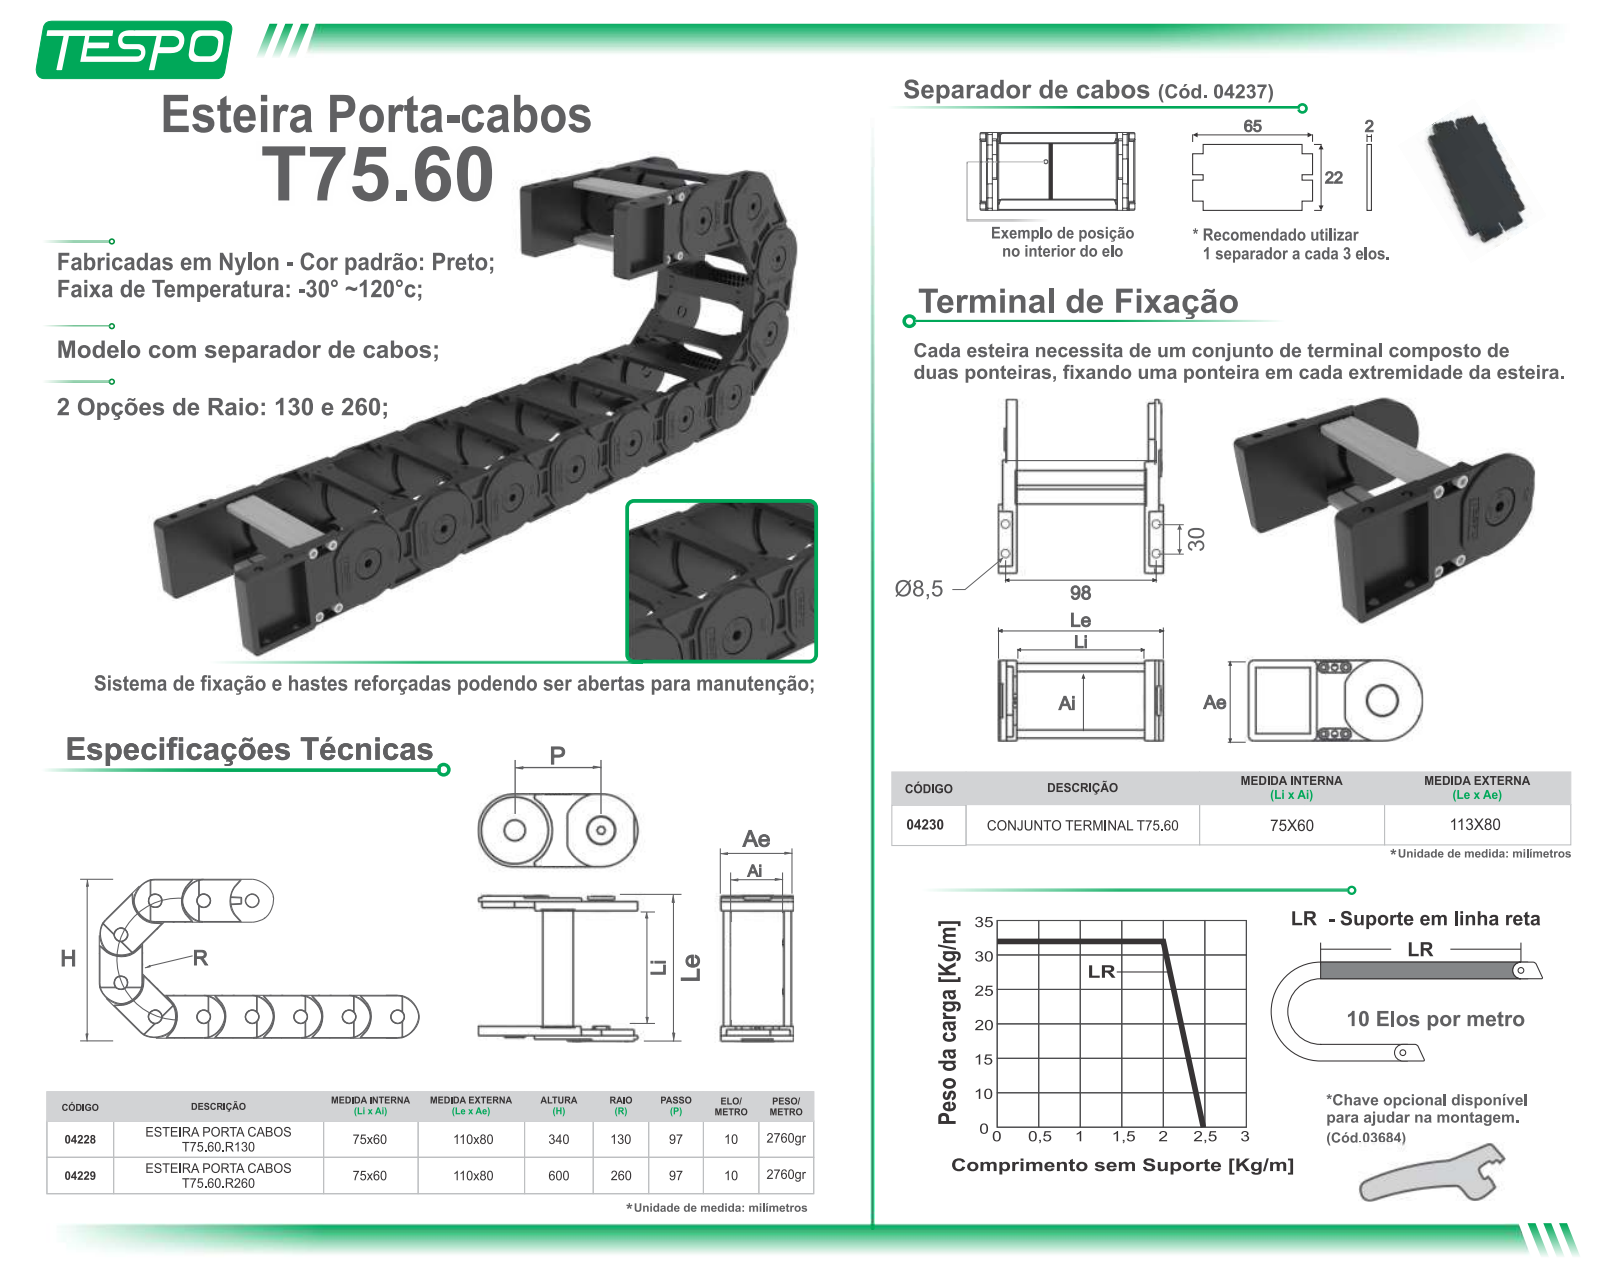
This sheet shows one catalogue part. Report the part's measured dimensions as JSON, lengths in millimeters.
{"step_written_by": "ST-DEVELOPER v15 (AUTOMOTIVE_DESIGN)", "units": "millimeters", "bodies": {"solids": 1, "faces": 74, "planar": 36, "cylindrical": 0, "other": 38}, "overall_size": [179, 108.6, 82], "volume_mm3": 282230, "surface_area_mm2": 84054, "face_to_face_distances": [16.8, 91.8, 13.3, 95.3, 3.5, 78.5, 13.1, 95.5, 3.7, 78.7]}
